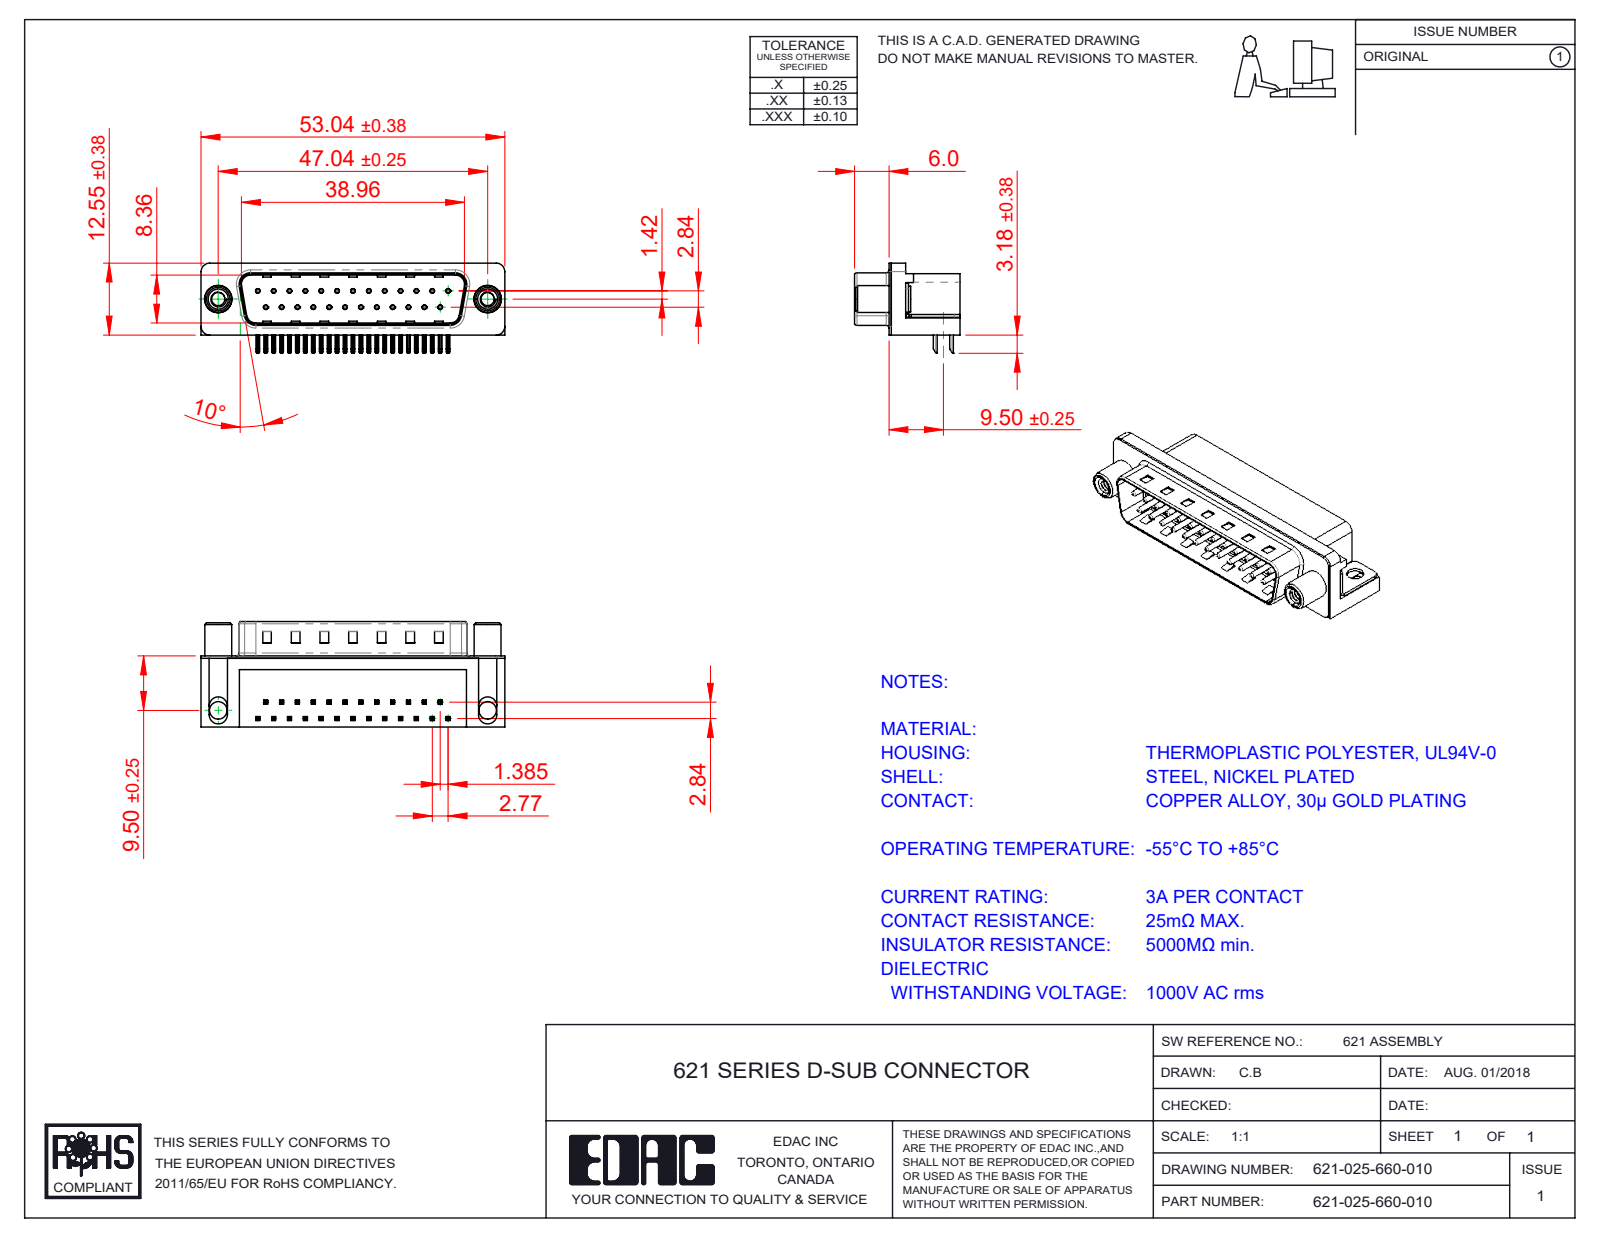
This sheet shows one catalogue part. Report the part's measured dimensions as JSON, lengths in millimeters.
{"part_name": "621 Housing_25 Socket; 621 Contact Bottom; 621 Round Threaded Standoff; 621 Shell_25 Socket (+3 more)", "step_written_by": "SolidWorks 2016 (CONFIG_CONTROL_DESIGN)", "units": "millimeters", "bodies": {"solids": 31, "faces": 2255, "planar": 1395, "cylindrical": 667, "other": 193}, "overall_size": [53.04, 18.4, 15.73], "volume_mm3": 6436, "surface_area_mm2": 7869, "round_holes": [[0.35, 25], [0.8, 25], [2.3, 2], [3.05, 2], [3.1, 2], [4, 2], [4.8, 2], [5, 2]], "round_bosses_or_shafts": [[0.75, 25], [4.9, 2], [4.7, 2], [4.5, 2], [3.85, 2]], "partial_cylinders_radius": [[0.25, 100], [0.12, 50], [1, 16], [0.5, 9], [1.6, 8], [1.5, 7], [0.9, 4], [2, 4]], "face_to_face_distances": [0.4, 12, 10.35, 2.1, 8.76, 10.46, 1.7, 10.86, 12.4, 2.9], "hole_center_spacings": [3.16, 2.77, 5.54, 8.31, 11.08, 13.85, 16.62, 5.03]}
